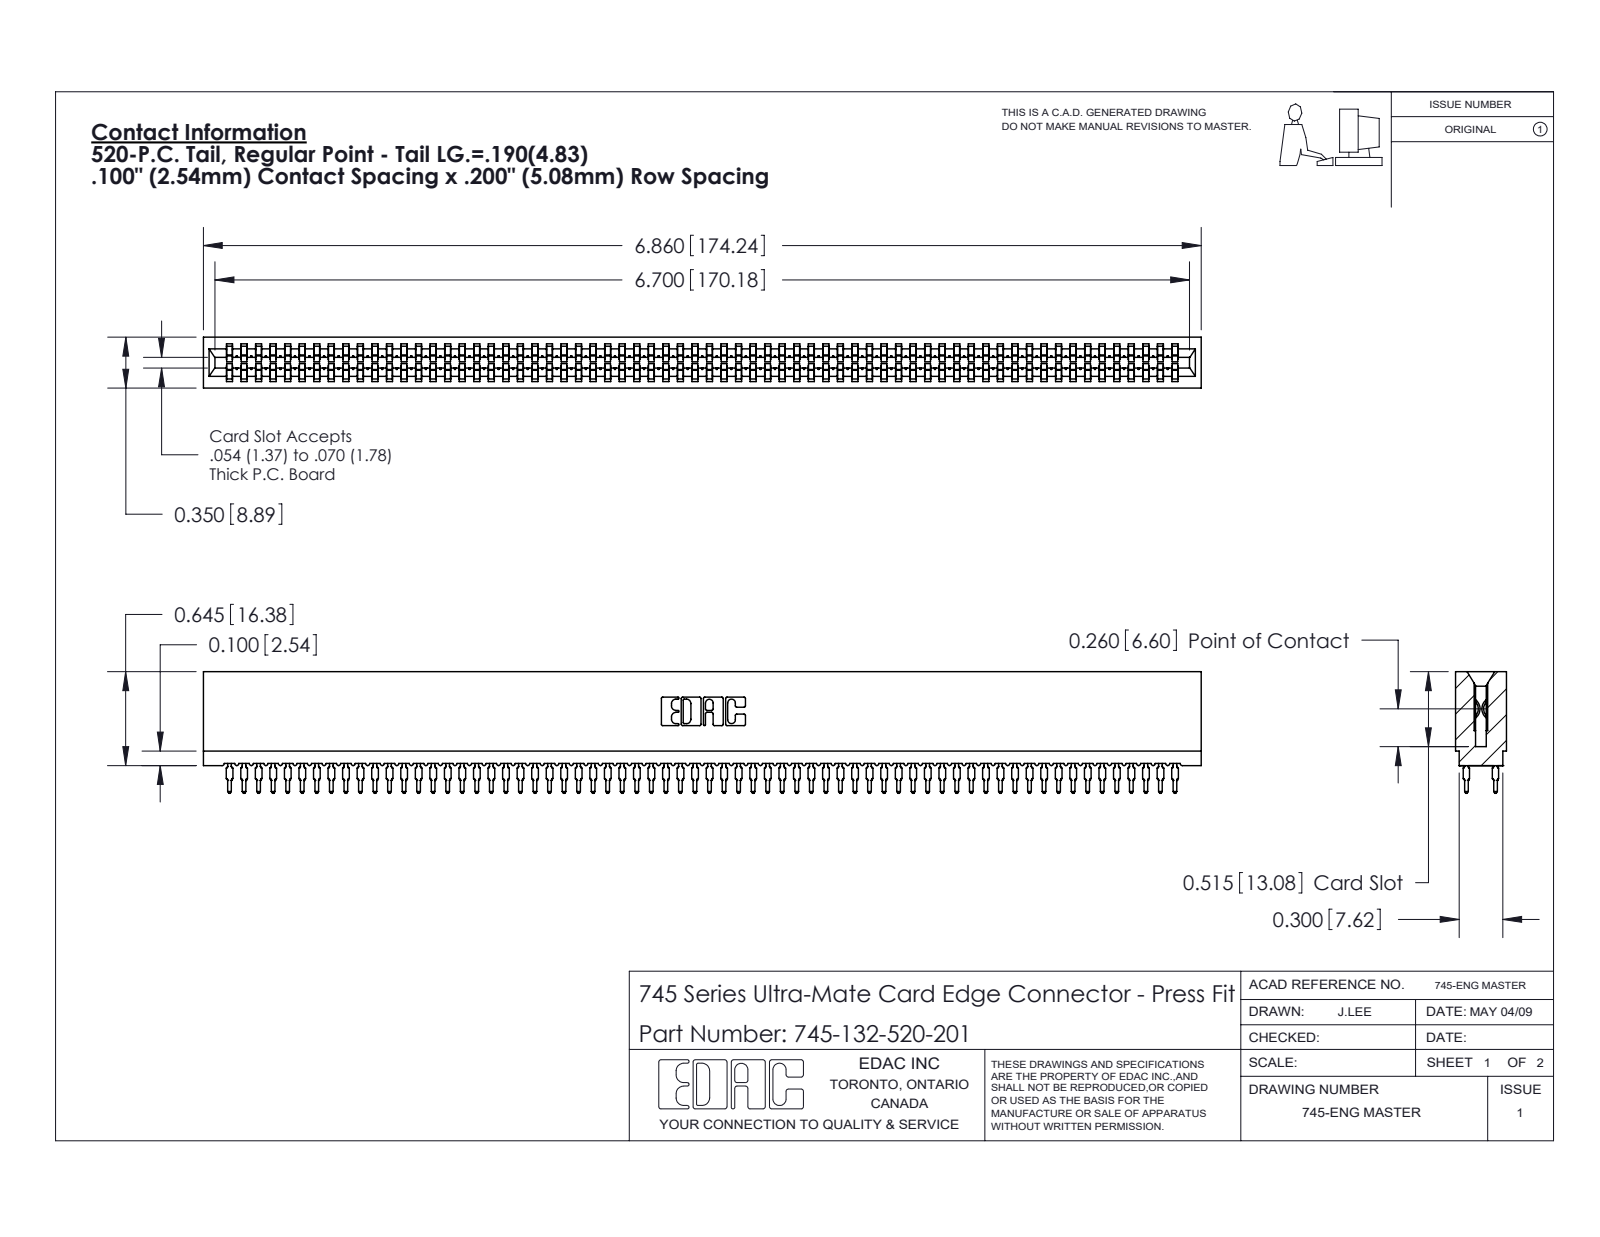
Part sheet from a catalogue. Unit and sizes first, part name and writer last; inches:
Units: inches
Overall size (bounding box): 6.86 × 0.836 × 0.35
Partial cylindrical surfaces — rounded edges, fillets, slot ends (radius × count): R0.021 ×264, R0.015 ×132, R0.01 ×22, R0.005 ×8, R0.011 ×8, R0.007 ×6, R0.031 ×6, R0.026 ×3
Main face-to-face distances: 0.35, 0.063, 0.287, 0.045, 0.305, 0.018, 0.243, 0.138, 0.212, 0.093
Volume: 0.942 in³ · Surface area: 48.56 in²
Bodies: 133 solids, 11909 faces (6127 planar, 2350 cylindrical, 3432 other)
Part name (STEP PRODUCT): 745 Part_Insulator Option - 01; 745-292-001_520; 745-132-520-201
STEP written by: SolidWorks 2020 (CONFIG_CONTROL_DESIGN)
